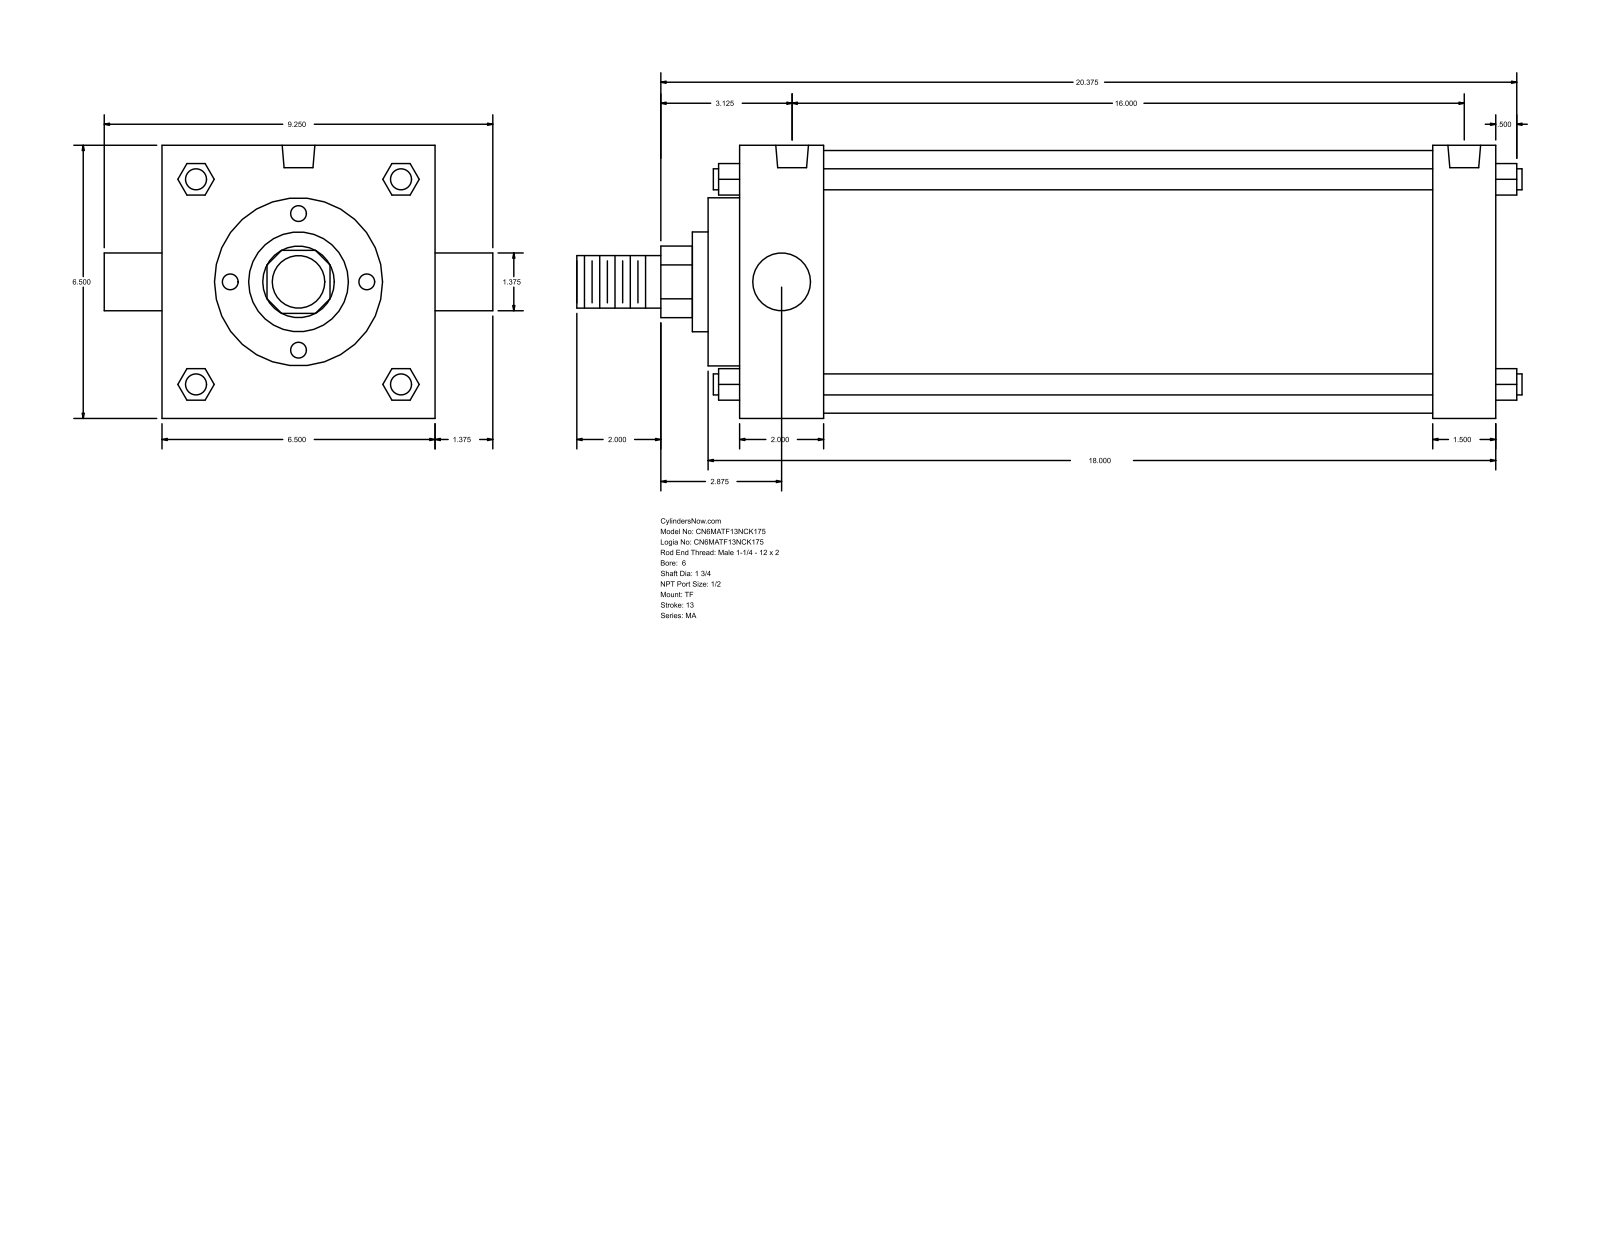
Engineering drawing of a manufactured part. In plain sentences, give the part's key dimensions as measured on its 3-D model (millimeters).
The part is named "MA_TF__0600_1.75". Its 3-D file was written by "GSSL Pune (CONFIG_CONTROL_DESIGN)". It is 0 solids with 122 faces: 93 planar, 29 cylindrical and 0 other. Overall it measures 571.5 by 234.95 by 165.1 millimeters. Round holes: 3 of diameter 17.46, 2 of diameter 19.77. Round bosses or shafts: 4 of diameter 12.7, 1 of diameter 158.75, 1 of diameter 101.6, 1 of diameter 60.33, 1 of diameter 44.45, 1 of diameter 34.92, 1 of diameter 31.75. Partial cylindrical surfaces (rounded edges, fillets, slot ends): 1 of radius 21.63. The main face-to-face distances are 165.1, 457.2, 19.05, 50.8, 406.4, 419.11, 368.31, 38.09, 69.85, 438.16. The hole center spacings are 406.39.
